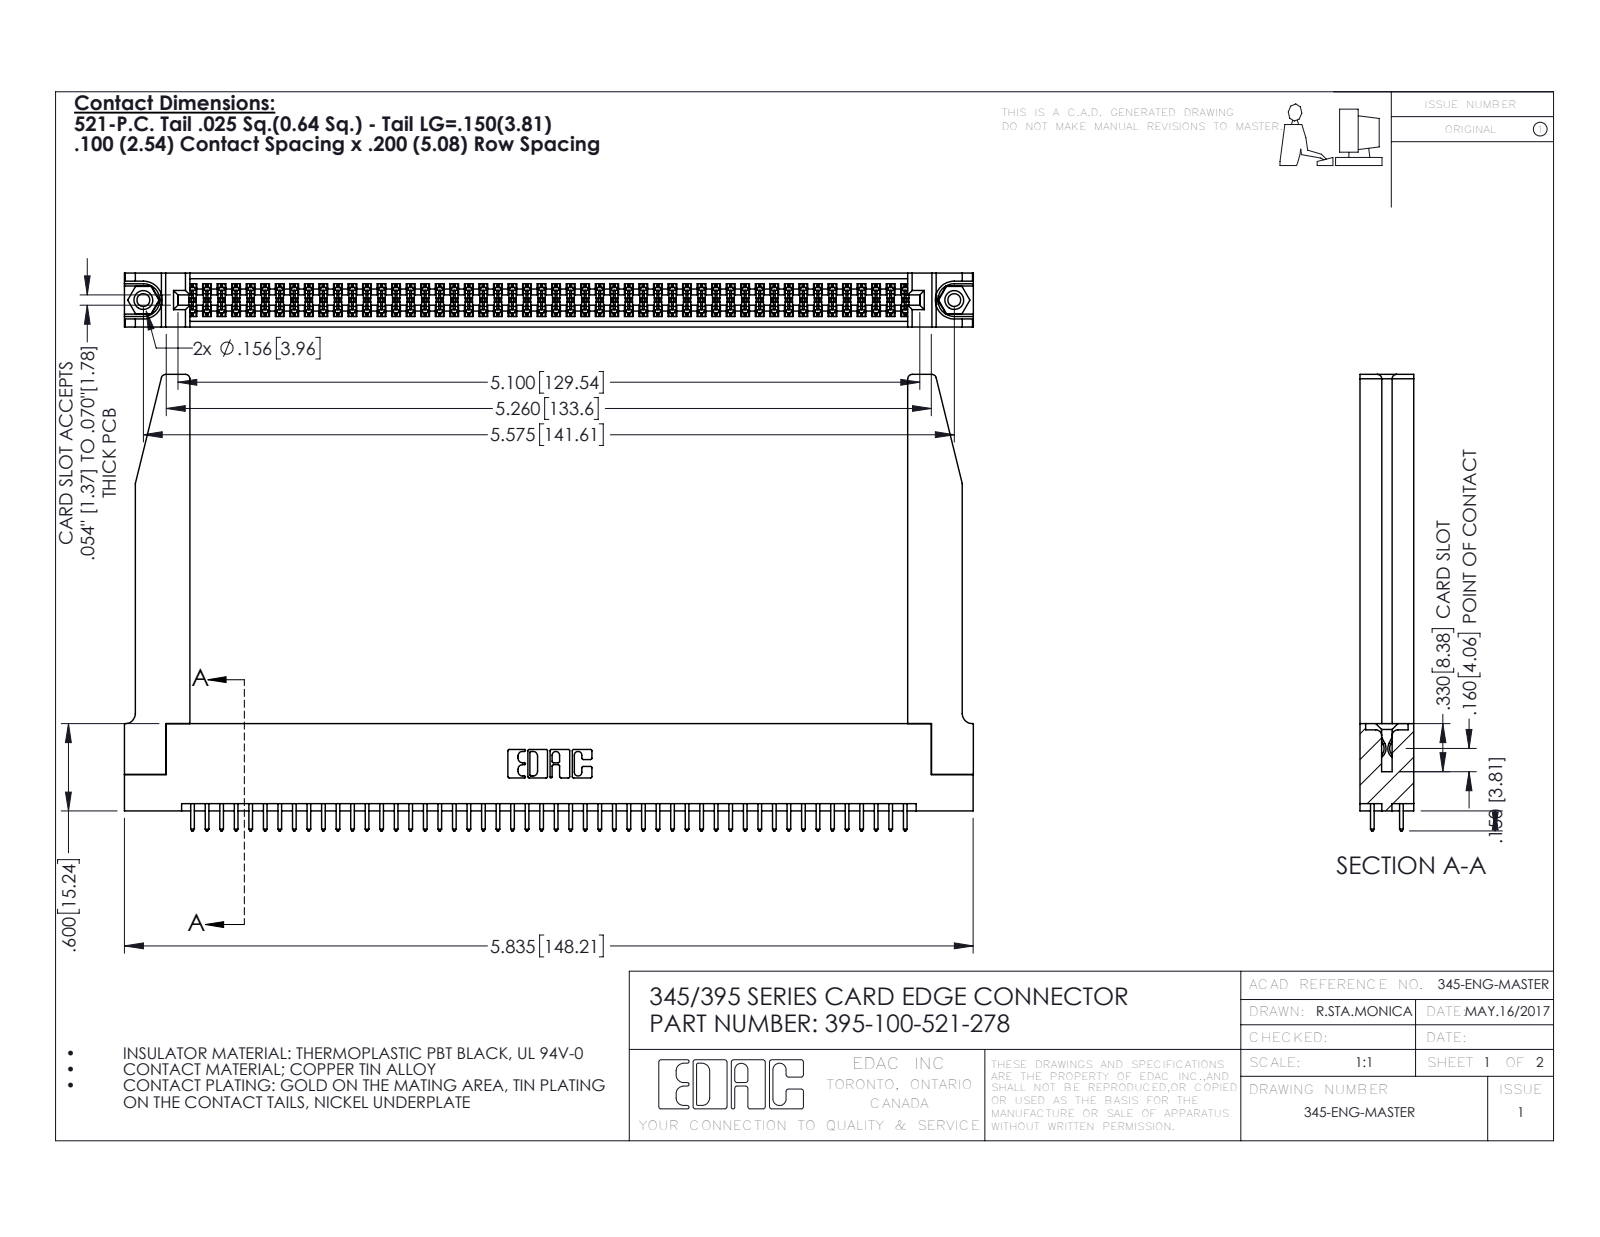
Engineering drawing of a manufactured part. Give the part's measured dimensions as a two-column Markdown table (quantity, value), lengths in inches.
| quantity | value |
| --- | --- |
| part name | 345-250-001_345-250-001-102; 345-220-078_345-220-078; 345-292-001_345-293-121; 345 Part_Flush Mounting Lugs - 0.156 Dia-TH (+1 more) |
| STEP written by | SolidWorks 2016 (CONFIG_CONTROL_DESIGN) |
| units | inches |
| bodies | 105 solids, 5360 faces (3522 planar, 1786 cylindrical, 52 other) |
| overall size | 5.836 × 3.137 × 0.37 |
| volume | 1.355 in³ |
| surface area | 43.5 in² |
| round holes (diameter × count) | 0.089 × 2, 0.125 × 2, 0.156 × 2, 0.064 × 1 |
| round bosses / shafts (diameter × count) | 0.155 × 2 |
| partial cylindrical surfaces (radius × count) | 0.006 × 150, 0.01 × 100, 0.01 × 22, 0.03 × 8, 0.007 × 6, 0.031 × 6, 0.026 × 3, 0.014 × 2 |
| main face-to-face distances | 0.072, 0.298, 0.37, 0.2, 0.098, 0.272, 0.025, 0.225, 0.175, 0.15 |
| hole center spacings | 0.27, 5.339, 5.575 |
